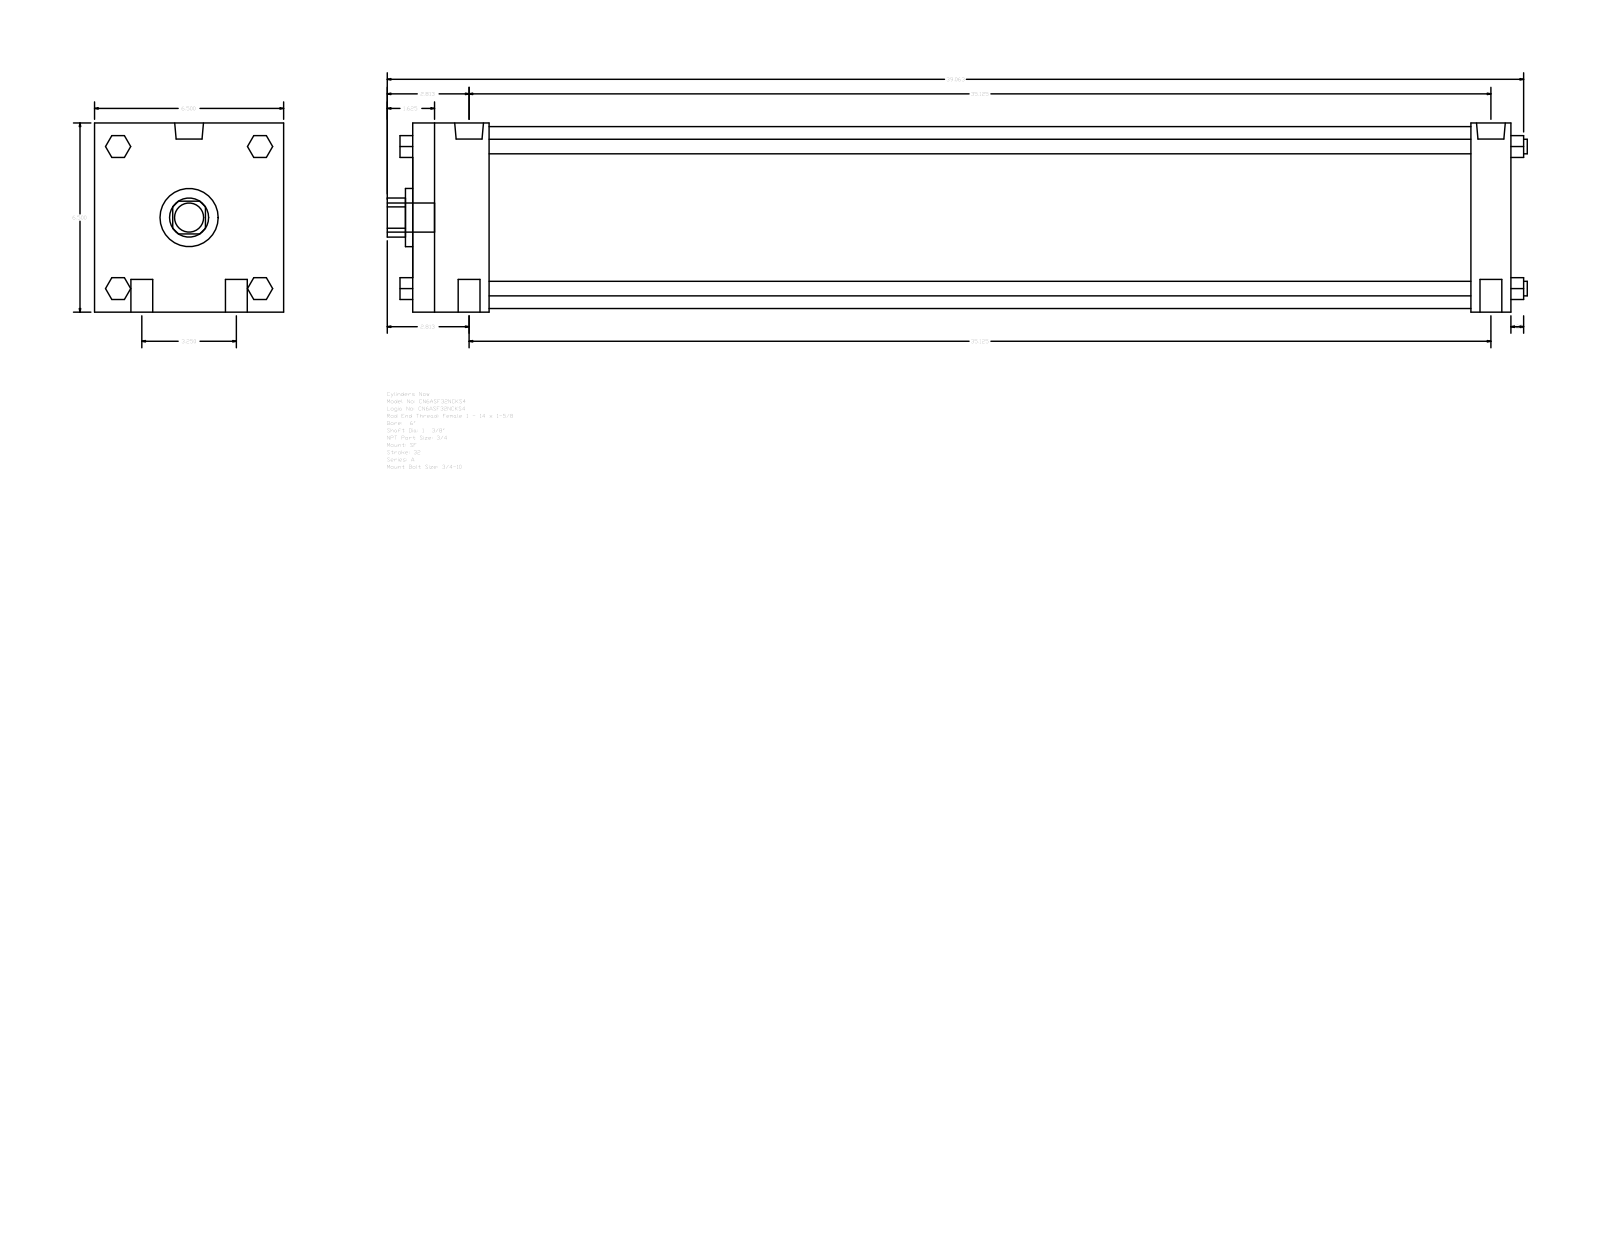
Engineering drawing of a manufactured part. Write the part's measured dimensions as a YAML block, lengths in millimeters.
part_name: "A_SF__0600_1.375"
step_written_by: "GSSL Pune (CONFIG_CONTROL_DESIGN)"
units: millimeters
bodies: {solids: 0, faces: 124, planar: 94, cylindrical: 30, other: 0}
overall_size: [995.36, 165.1, 165.1]
round_holes:
  - {diameter: 34.92, count: 1}
  - {diameter: 50.8, count: 1}
  - {diameter: 158.75, count: 1}
round_bosses_or_shafts:
  - {diameter: 19.05, count: 4}
  - {diameter: 12.7, count: 4}
  - {diameter: 25.12, count: 2}
  - {diameter: 15.08, count: 2}
  - {diameter: 25.4, count: 1}
partial_cylinders:
  - {radius: 17.06, count: 1}
face_to_face_distances: [165.1, 958.85, 923.92, 34.93, 66.67, 857.25, 892.18, 19.05, 61.97, 107.34]
